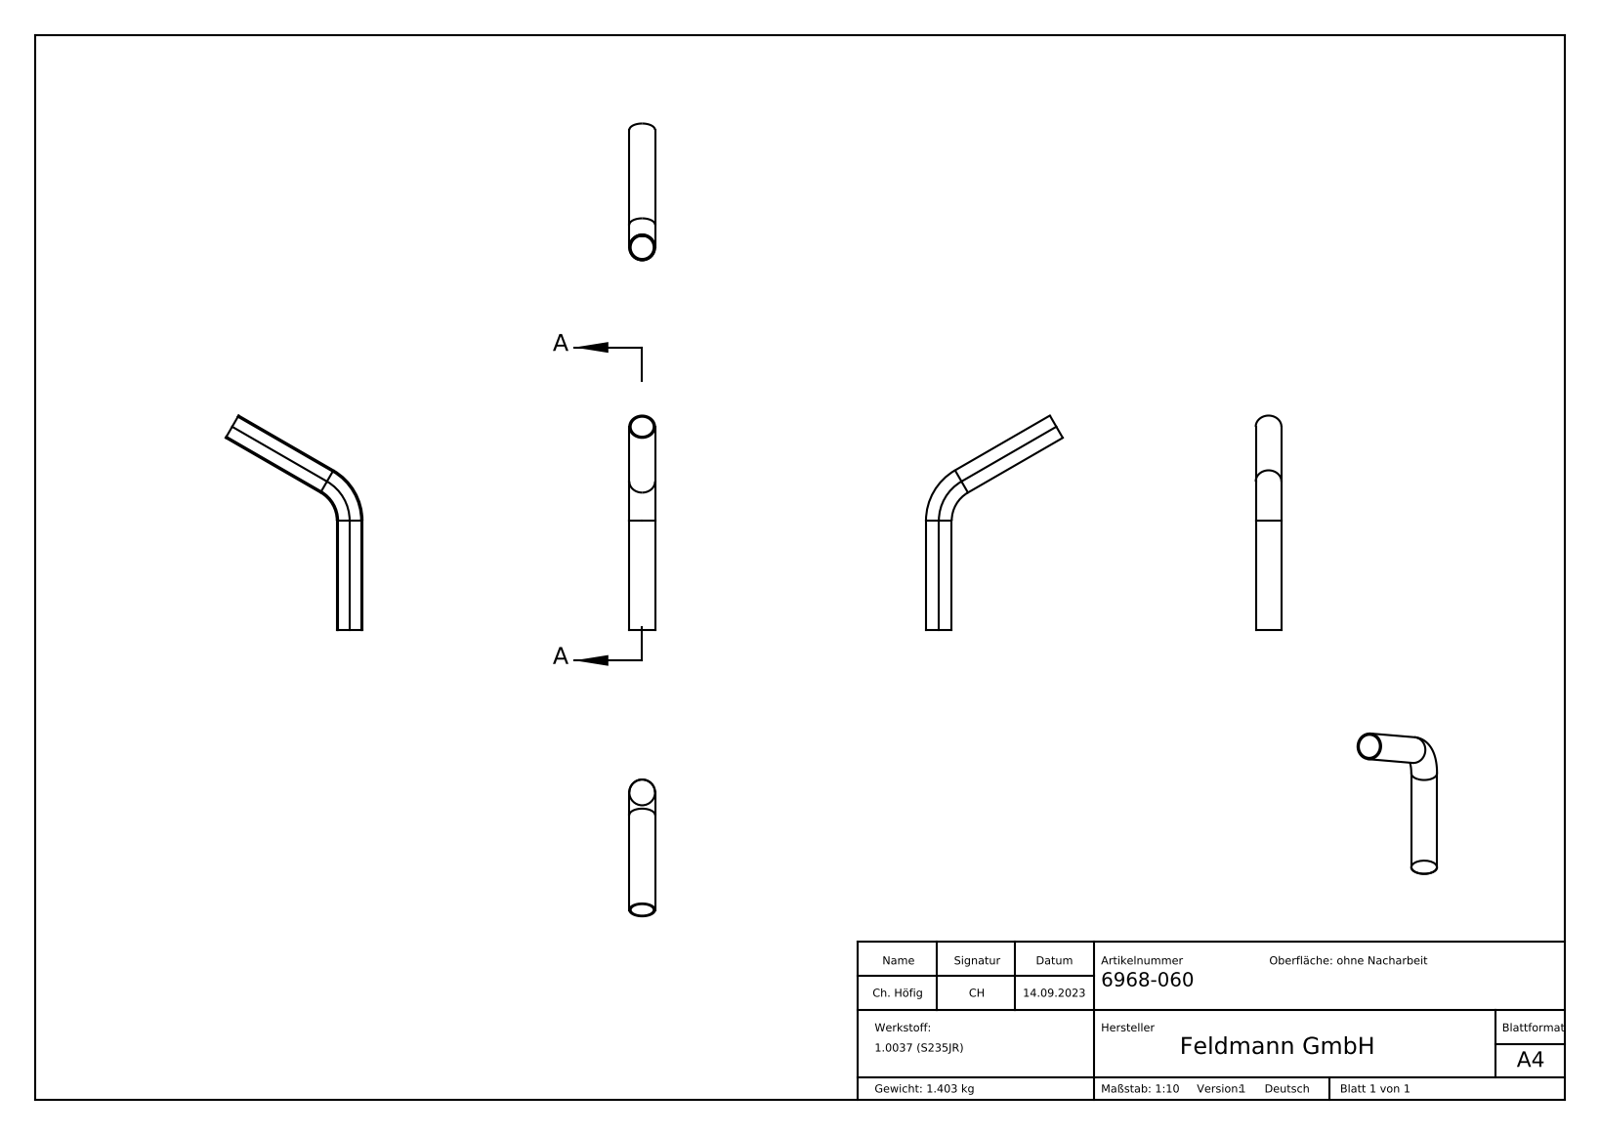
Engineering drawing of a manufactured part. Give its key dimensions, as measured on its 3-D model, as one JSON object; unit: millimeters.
{"part_name": "6968-060", "step_written_by": "SolidWorks 2018 (CONFIG_CONTROL_DESIGN)", "units": "millimeters", "bodies": {"solids": 1, "faces": 224, "planar": 99, "cylindrical": 4, "other": 121}, "overall_size": [402.77, 256.69, 48.3], "volume_mm3": 179856, "surface_area_mm2": 144608, "round_holes": [[43.3, 2]], "round_bosses_or_shafts": [[48.3, 2]], "face_to_face_distances": [0.5, 0.55, 0.53, 0.34, 0.31, 0.45, 0.58, 0.39, 0.48, 0.47]}
